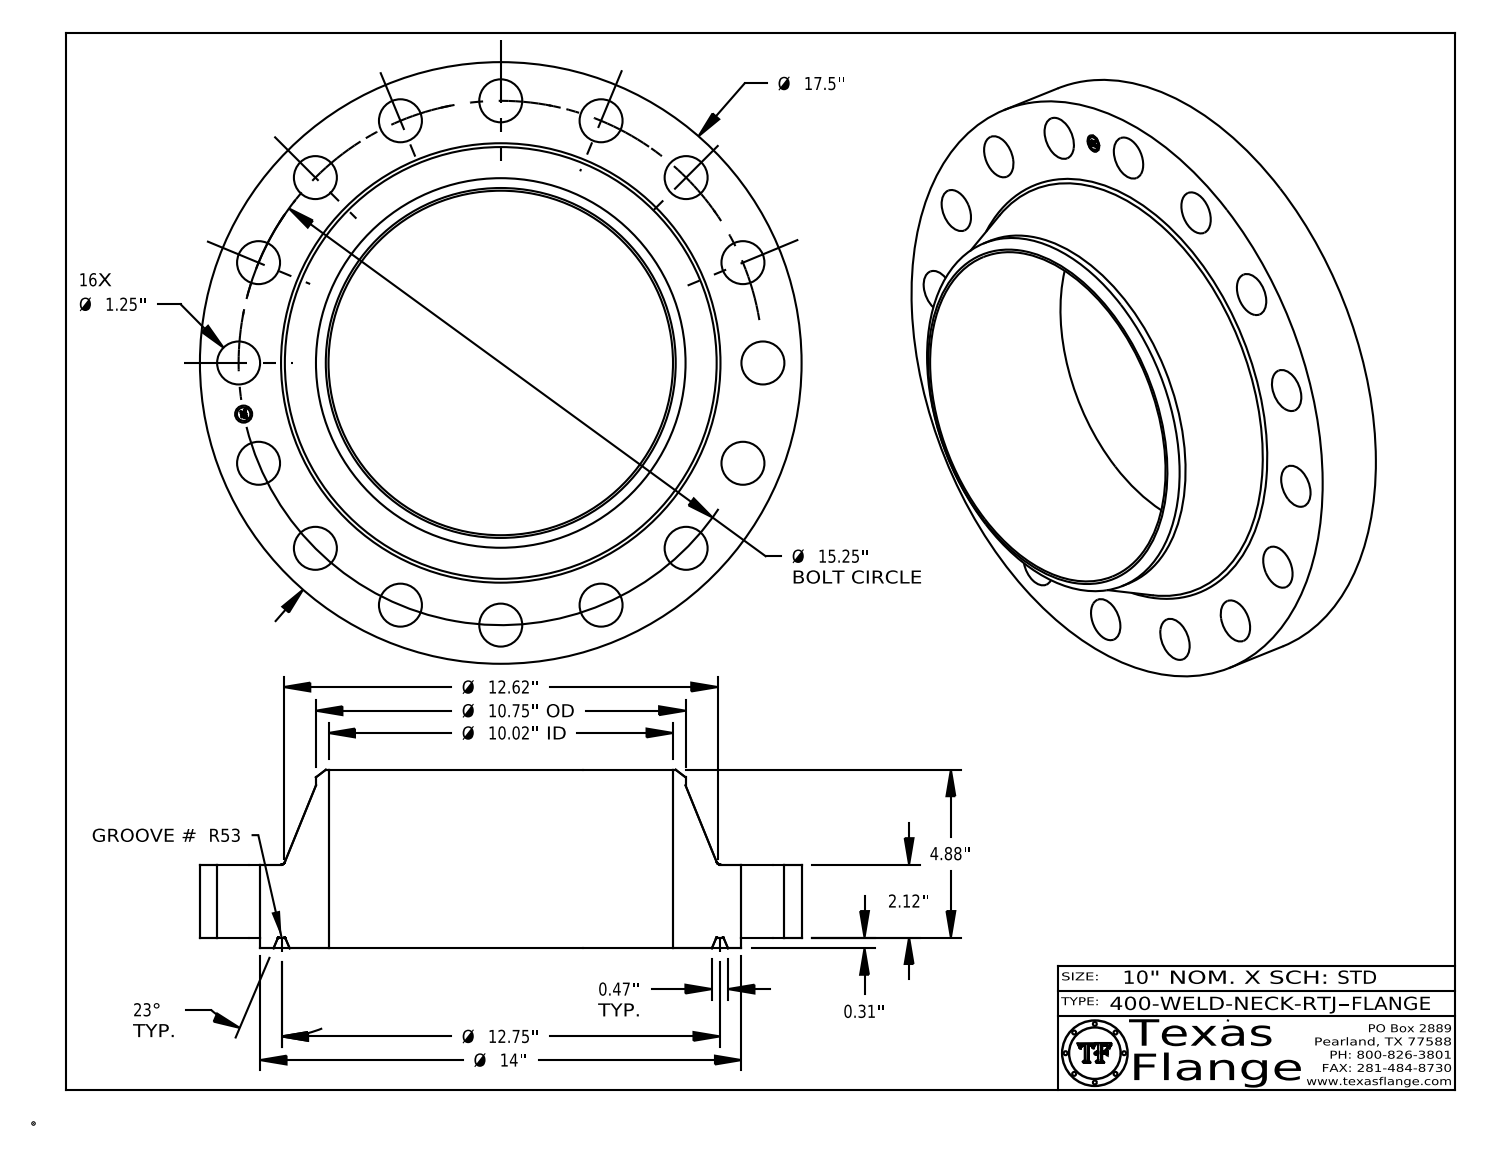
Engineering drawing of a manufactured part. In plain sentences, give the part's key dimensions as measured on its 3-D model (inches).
The part is named "400-WELD-NECK-RTJ". Its 3-D file was written by "CATIA V5 STEP AP214 (AUTOMOTIVE_DESIGN)". It is 1 solid with 445 faces: 371 planar, 60 cylindrical and 14 other. Overall it measures 17.5 by 17.5 by 5.193 inches. Its volume is 390.8 cubic inches and its surface area 794 square inches. Round holes: 16 of diameter 1.25, 1 of diameter 0.495, 1 of diameter 10.02. Round bosses or shafts: 8 of diameter 0.03, 1 of diameter 17.5, 1 of diameter 14, 1 of diameter 10.75, 1 of diameter 0.39. The main face-to-face distances are 2.12, 0.313, 2.433, 5.193, 4.88, 2.76, 0.015, 2.418, 2.105, 2.775. The hole center spacings are 8.472, 10.783, 14.957, 14.089, 7.625, 2.975, 2.975, 5.836.
